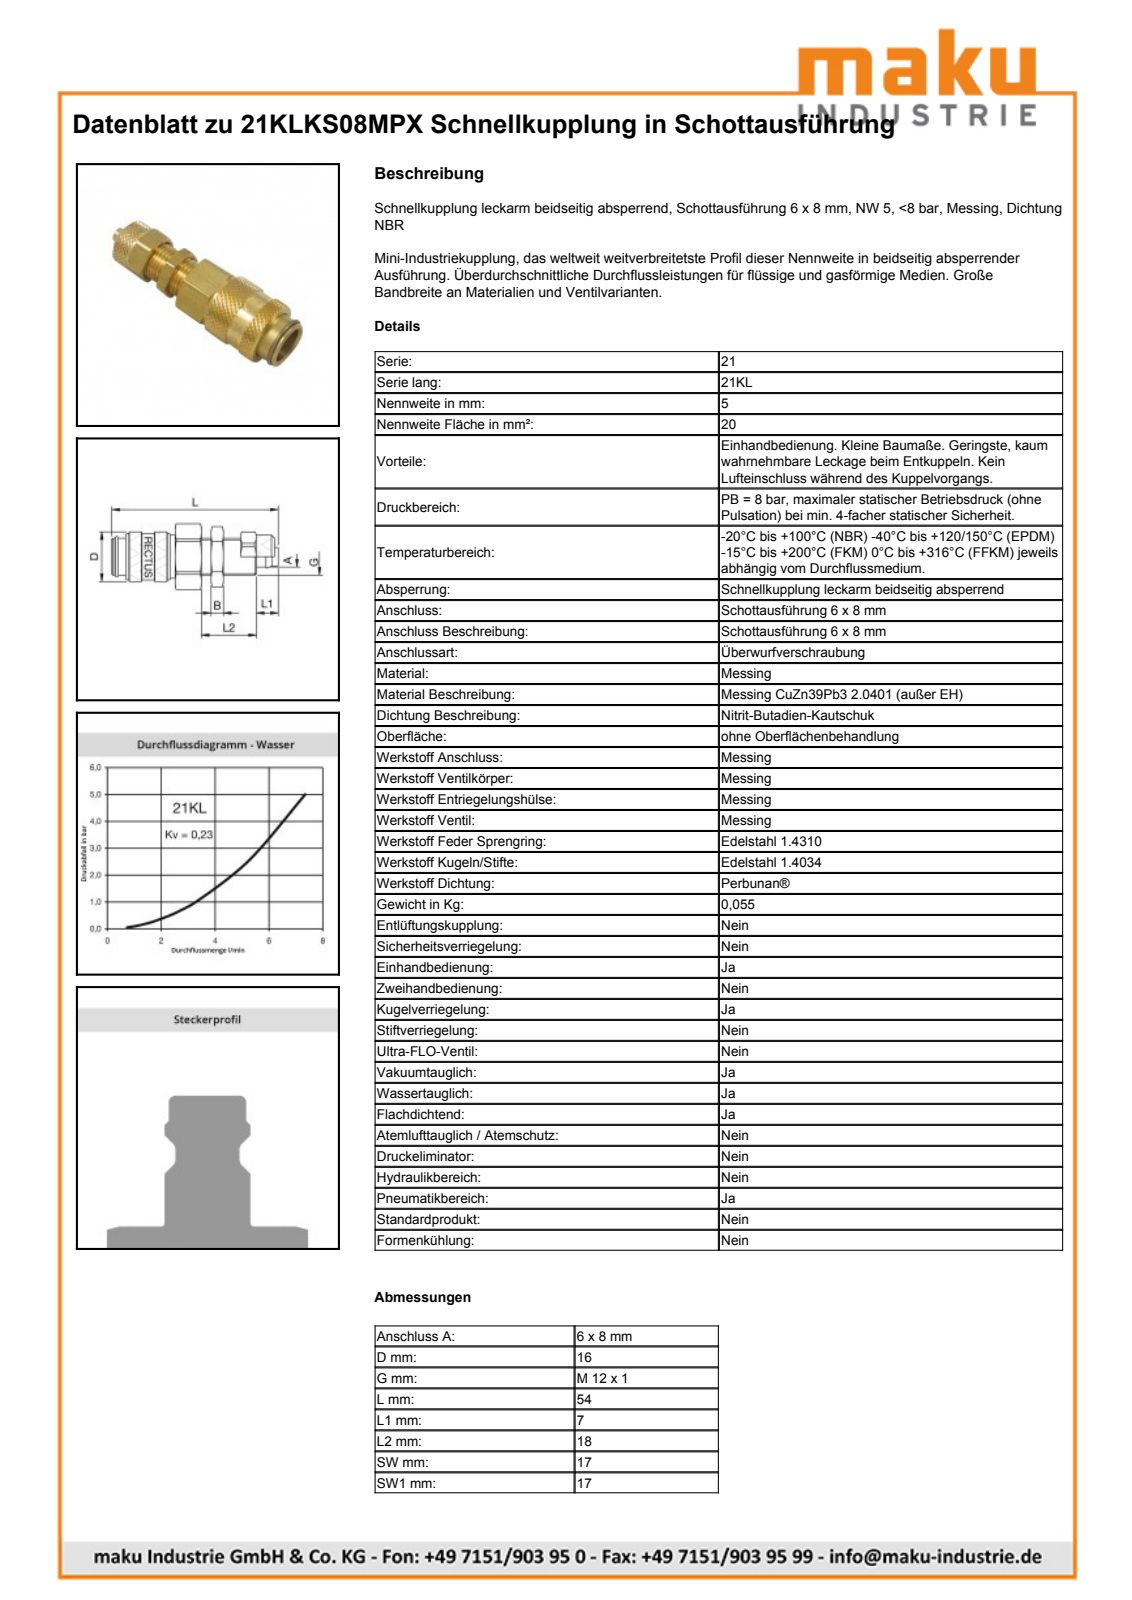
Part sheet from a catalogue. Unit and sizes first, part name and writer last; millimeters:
Units: millimetres
Overall size (bounding box): 54.15 × 19.05 × 18.37
Round holes (diameter × count): ⌀8.25 ×1, ⌀11.15 ×1, ⌀12.15 ×1, ⌀14 ×1
Round bosses / shafts (diameter × count): ⌀16.15 ×1, ⌀15.1 ×1, ⌀12 ×1, ⌀11.4 ×1, ⌀11.15 ×1, ⌀10.82 ×1, ⌀6.7 ×1, ⌀6.05 ×1
Partial cylindrical surfaces — rounded edges, fillets, slot ends (radius × count): R7.45 ×1, R7.75 ×1, R9.57 ×1
Main face-to-face distances: 17, 29.15, 4, 14, 38.21, 9.06, 34.21, 5.06, 20.6, 8.55
Volume: 8 769 mm³ · Surface area: 5 268 mm²
Bodies: 2 solids, 525 faces (168 planar, 79 cylindrical, 278 other)
Part name (STEP PRODUCT): D113608
STEP written by: Autodesk Inventor 2013 (AUTOMOTIVE_DESIGN)
